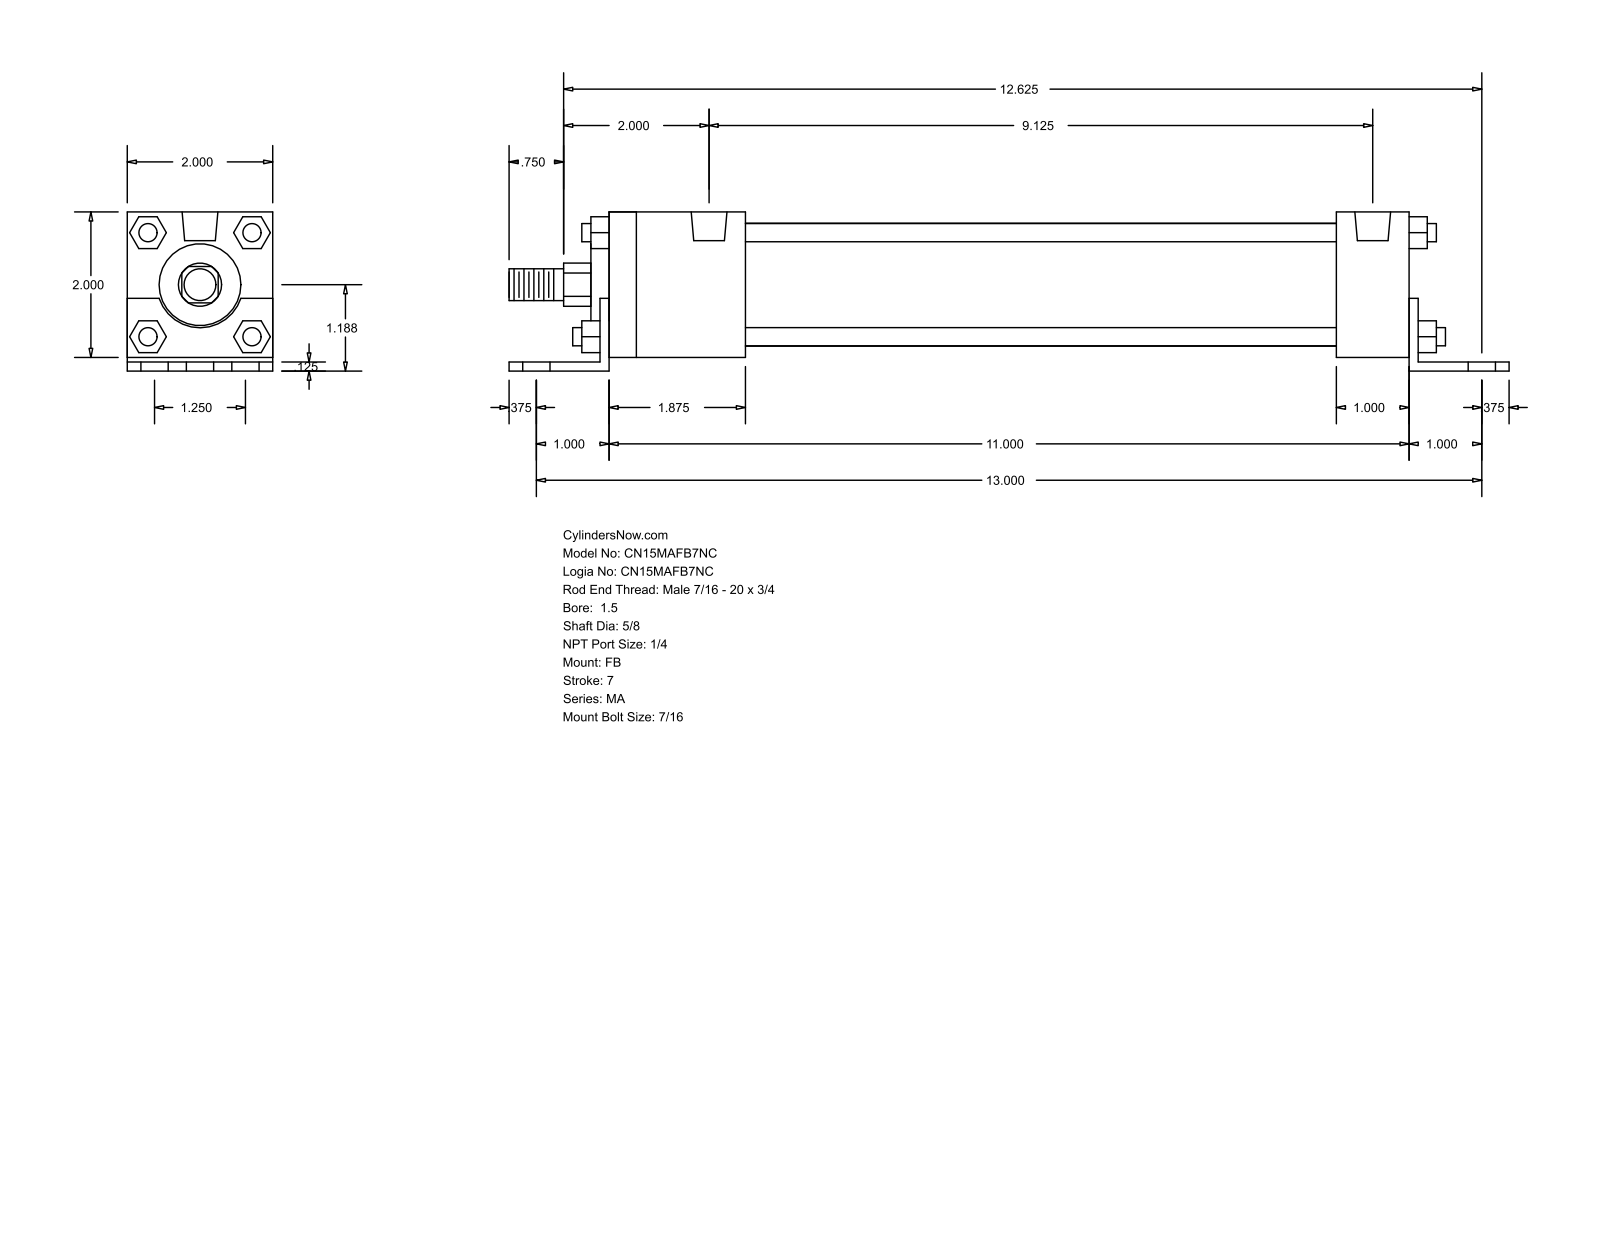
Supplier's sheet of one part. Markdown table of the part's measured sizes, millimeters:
| quantity | value |
| --- | --- |
| part name | MA_FB__0150_0.625 |
| STEP written by | GSSL Pune (CONFIG_CONTROL_DESIGN) |
| units | millimeters |
| bodies | 0 solids, 140 faces (105 planar, 35 cylindrical, 0 other) |
| overall size | 349.25 × 55.56 × 50.8 |
| round holes (diameter × count) | 11.11 × 6, 7.94 × 4, 12.49 × 2 |
| round bosses / shafts (diameter × count) | 6.35 × 4, 42.93 × 1, 28.57 × 1, 15.88 × 1, 11.11 × 1 |
| partial cylindrical surfaces (radius × count) | 7.54 × 1, 15.05 × 1 |
| main face-to-face distances | 50.8, 3.17, 4.76, 55.56, 1.59, 52.39, 3.18, 282.57, 6.35, 288.92 |
| hole center spacings | 15.88, 330.59, 330.21, 31.76, 41.29, 62.38, 231.77, 270.35 |
